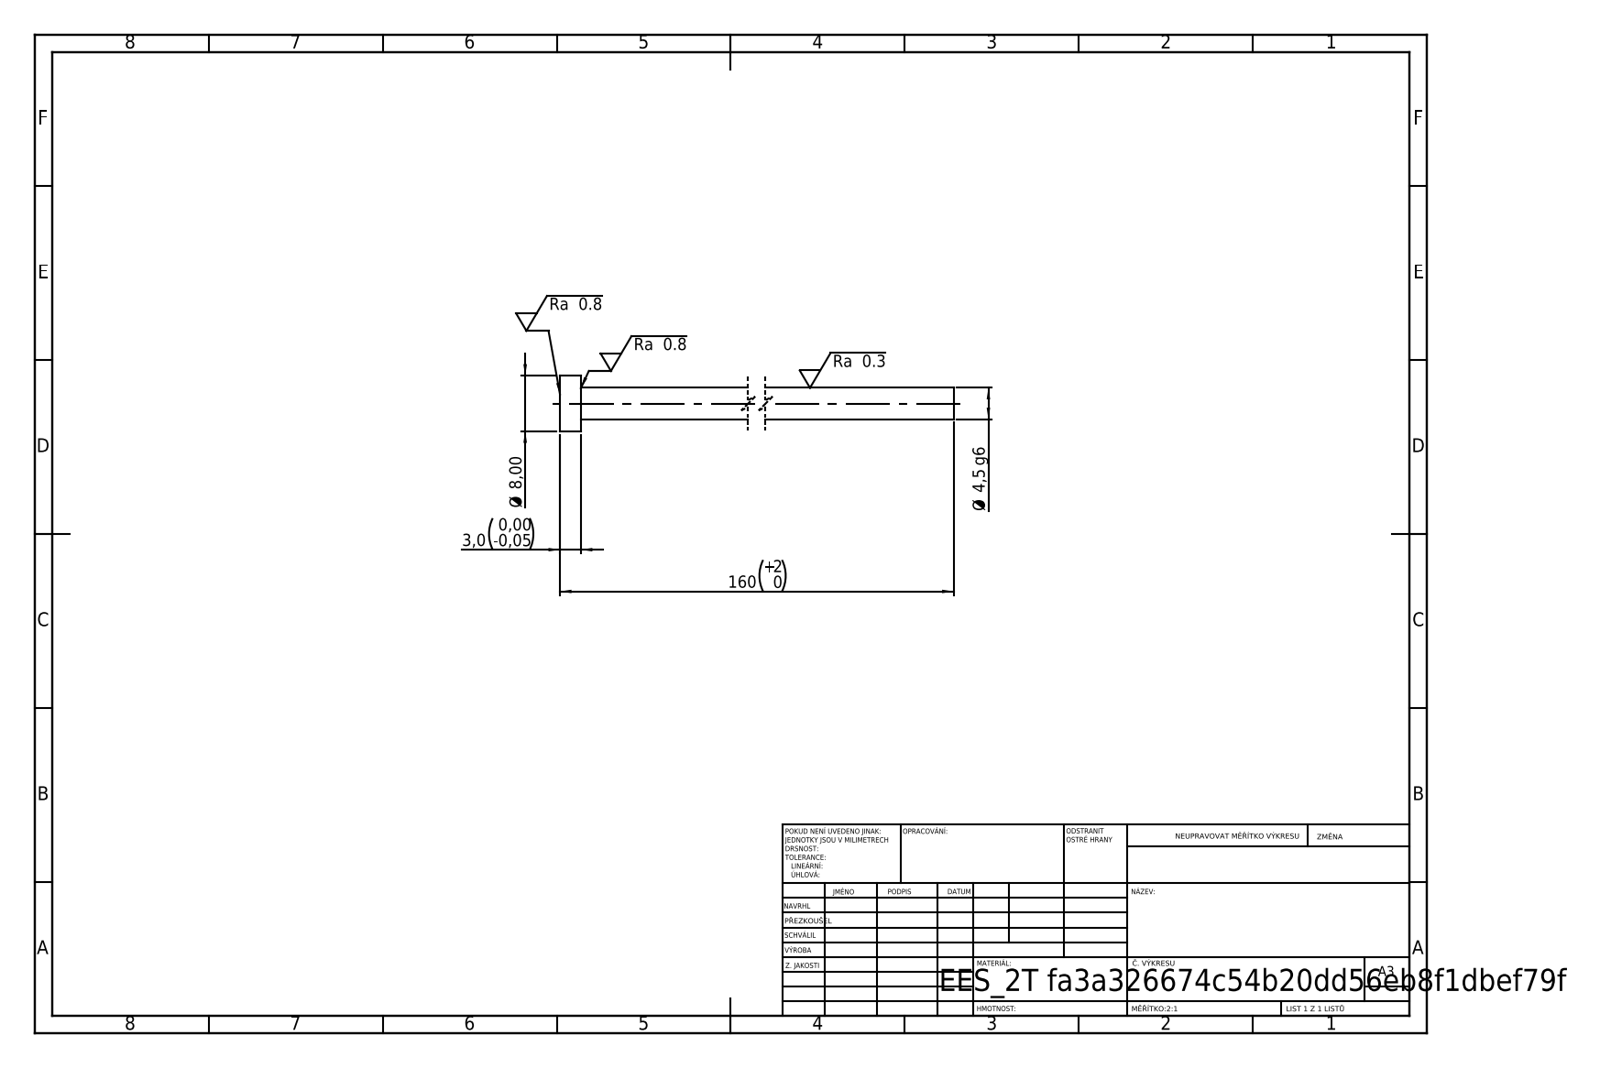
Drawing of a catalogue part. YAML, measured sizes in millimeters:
step_written_by: "SolidWorks 2019 (CONFIG_CONTROL_DESIGN)"
units: millimeters
bodies: {solids: 1, faces: 7, planar: 3, cylindrical: 4, other: 0}
overall_size: [160, 8, 8]
volume: 2648
surface_area: 2395
round_bosses_or_shafts:
  - {diameter: 8, count: 1}
  - {diameter: 4.5, count: 1}
face_to_face_distances: [3, 160, 157]
